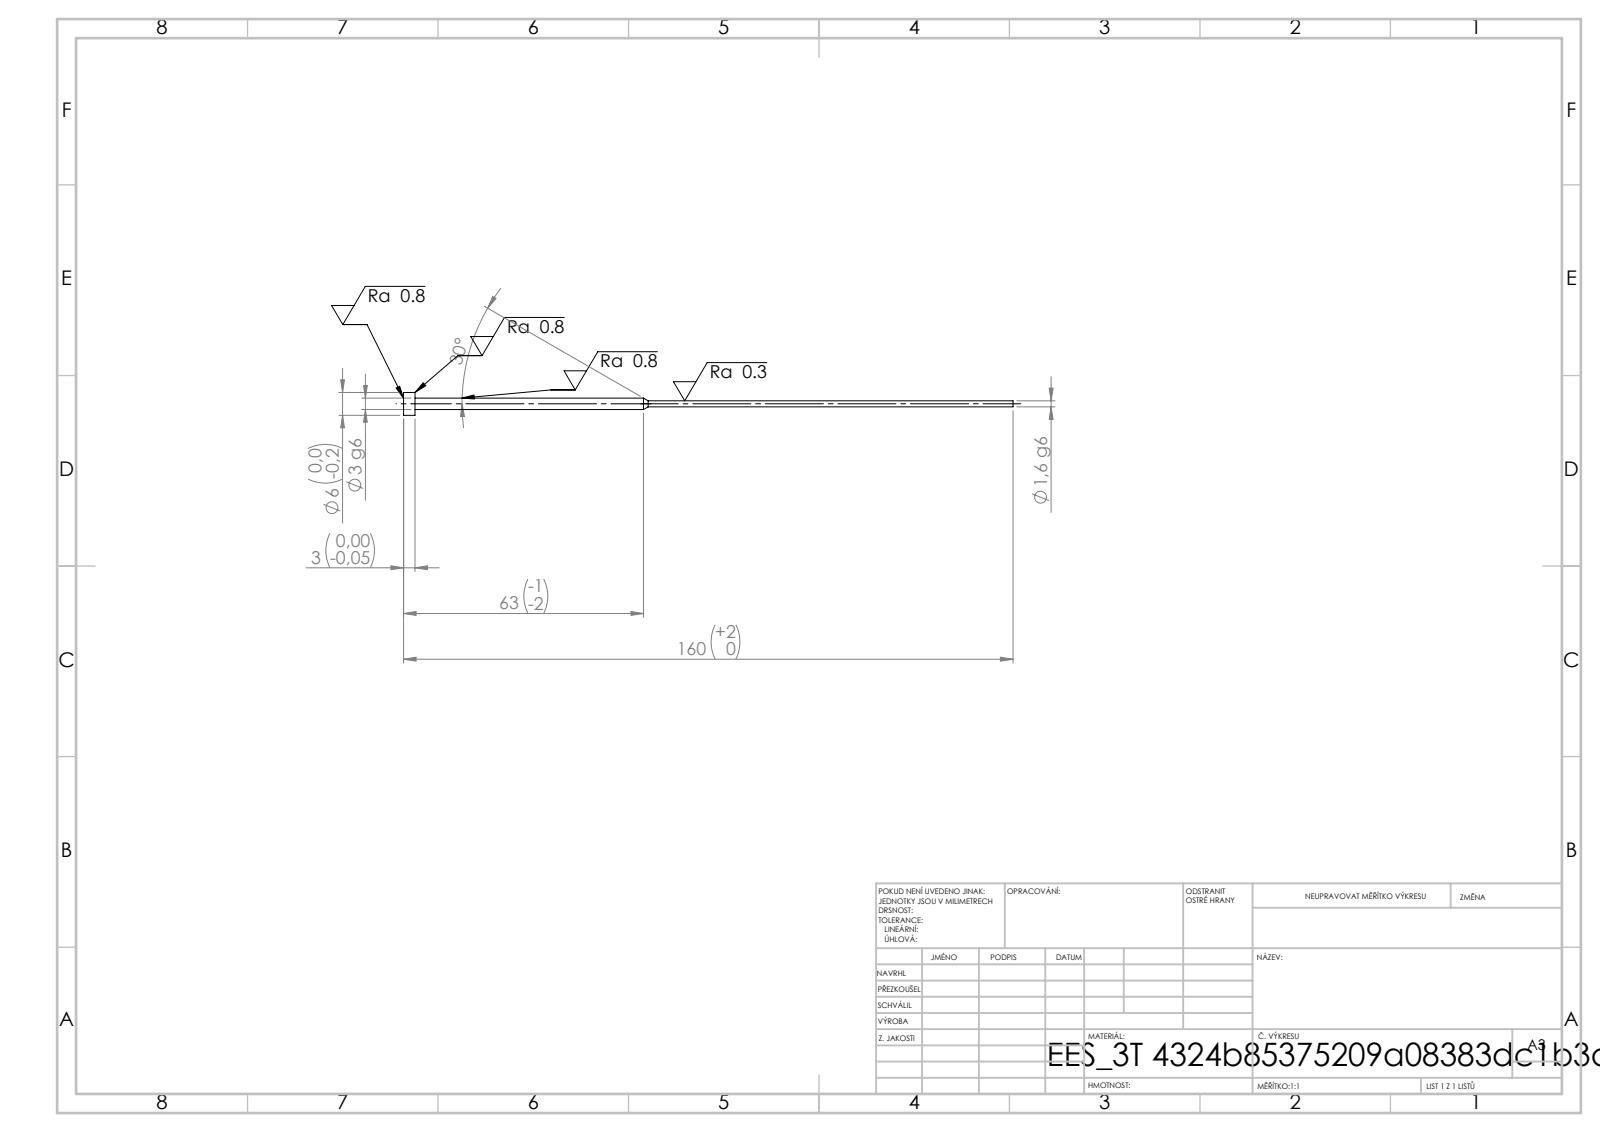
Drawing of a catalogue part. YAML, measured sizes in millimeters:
step_written_by: "SolidWorks 2019 (CONFIG_CONTROL_DESIGN)"
units: millimeters
bodies: {solids: 1, faces: 11, planar: 3, cylindrical: 6, other: 2}
overall_size: [160, 6, 6]
volume: 707
surface_area: 1165
round_bosses_or_shafts:
  - {diameter: 6, count: 1}
  - {diameter: 3, count: 1}
  - {diameter: 1.6, count: 1}
face_to_face_distances: [3, 157, 160]
